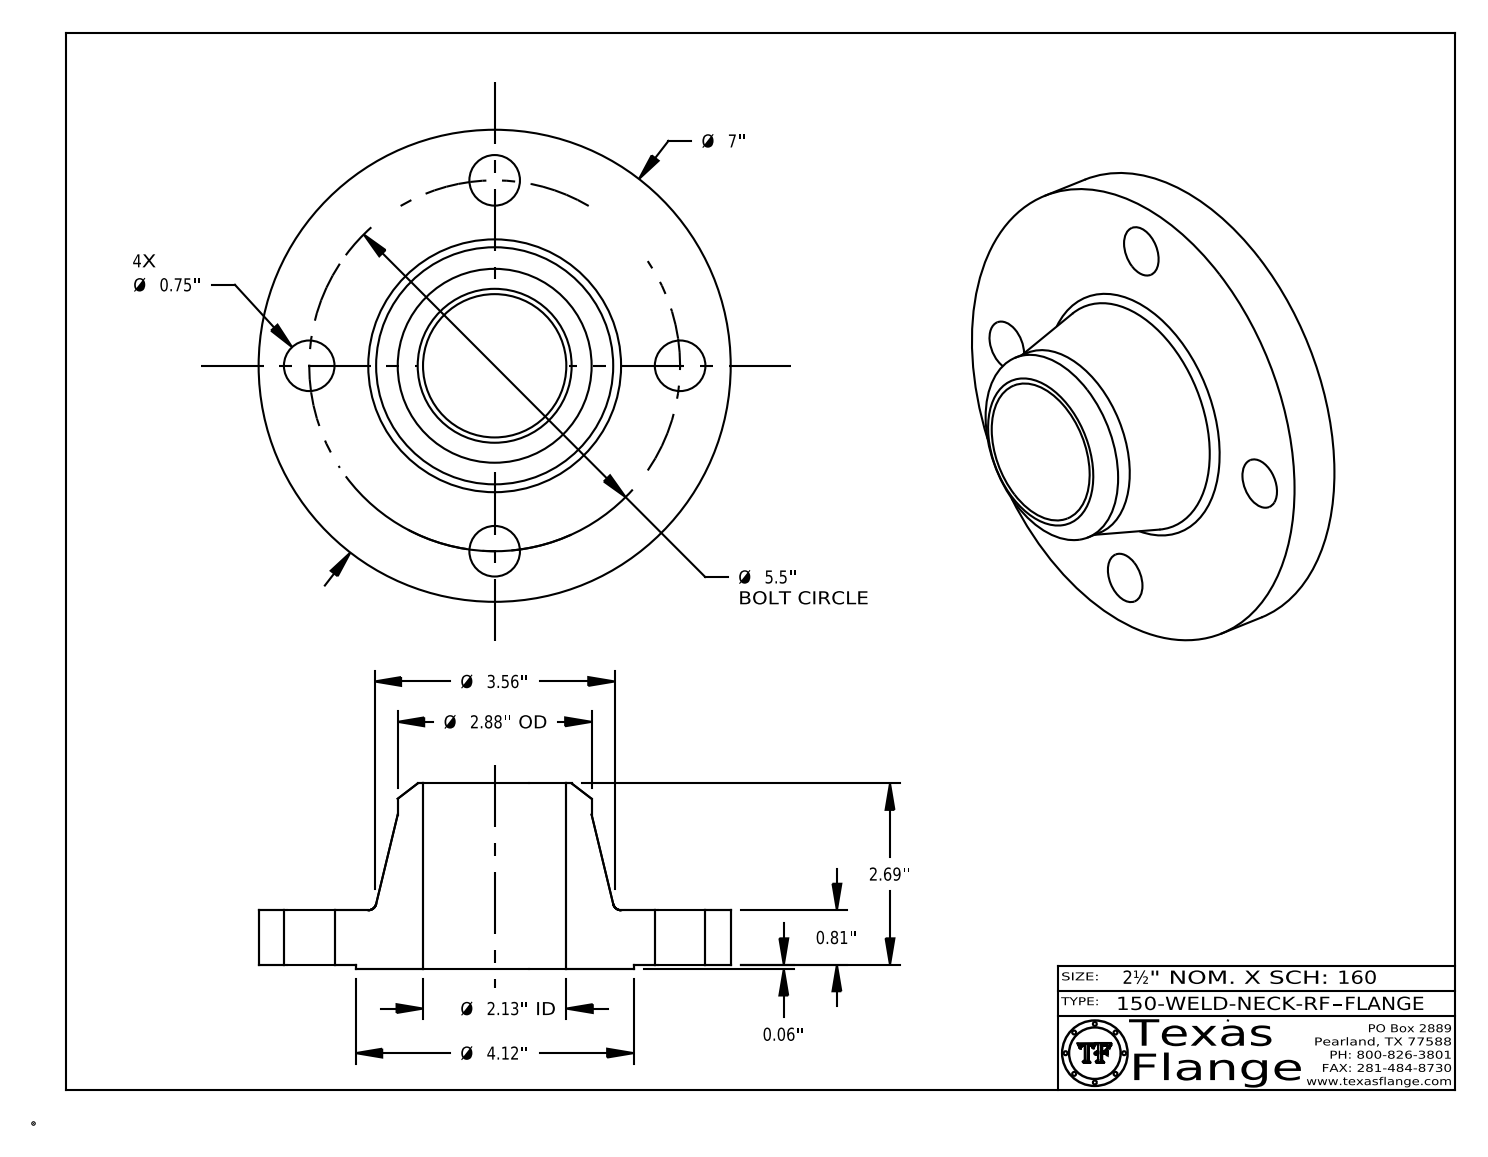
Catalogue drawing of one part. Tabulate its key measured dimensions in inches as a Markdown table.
| quantity | value |
| --- | --- |
| part name | 150-WELD-NECK-RF |
| STEP written by | CATIA V5 STEP AP214 (AUTOMOTIVE_DESIGN) |
| units | inches |
| bodies | 1 solid, 411 faces (369 planar, 36 cylindrical, 6 other) |
| overall size | 7 × 7 × 2.753 |
| volume | 35.12 in³ |
| surface area | 124.8 in² |
| round holes (diameter × count) | 0.75 × 4, 0.495 × 1, 2.125 × 1 |
| round bosses / shafts (diameter × count) | 0.03 × 8, 7 × 1, 4.12 × 1, 2.875 × 1, 0.39 × 1 |
| main face-to-face distances | 0.81, 0.063, 0.872, 2.753, 2.69, 1.88, 0.857, 0.795, 0.015, 1.895 |
| hole center spacings | 2.75, 3.889, 2.105, 5.081, 5.5 |
